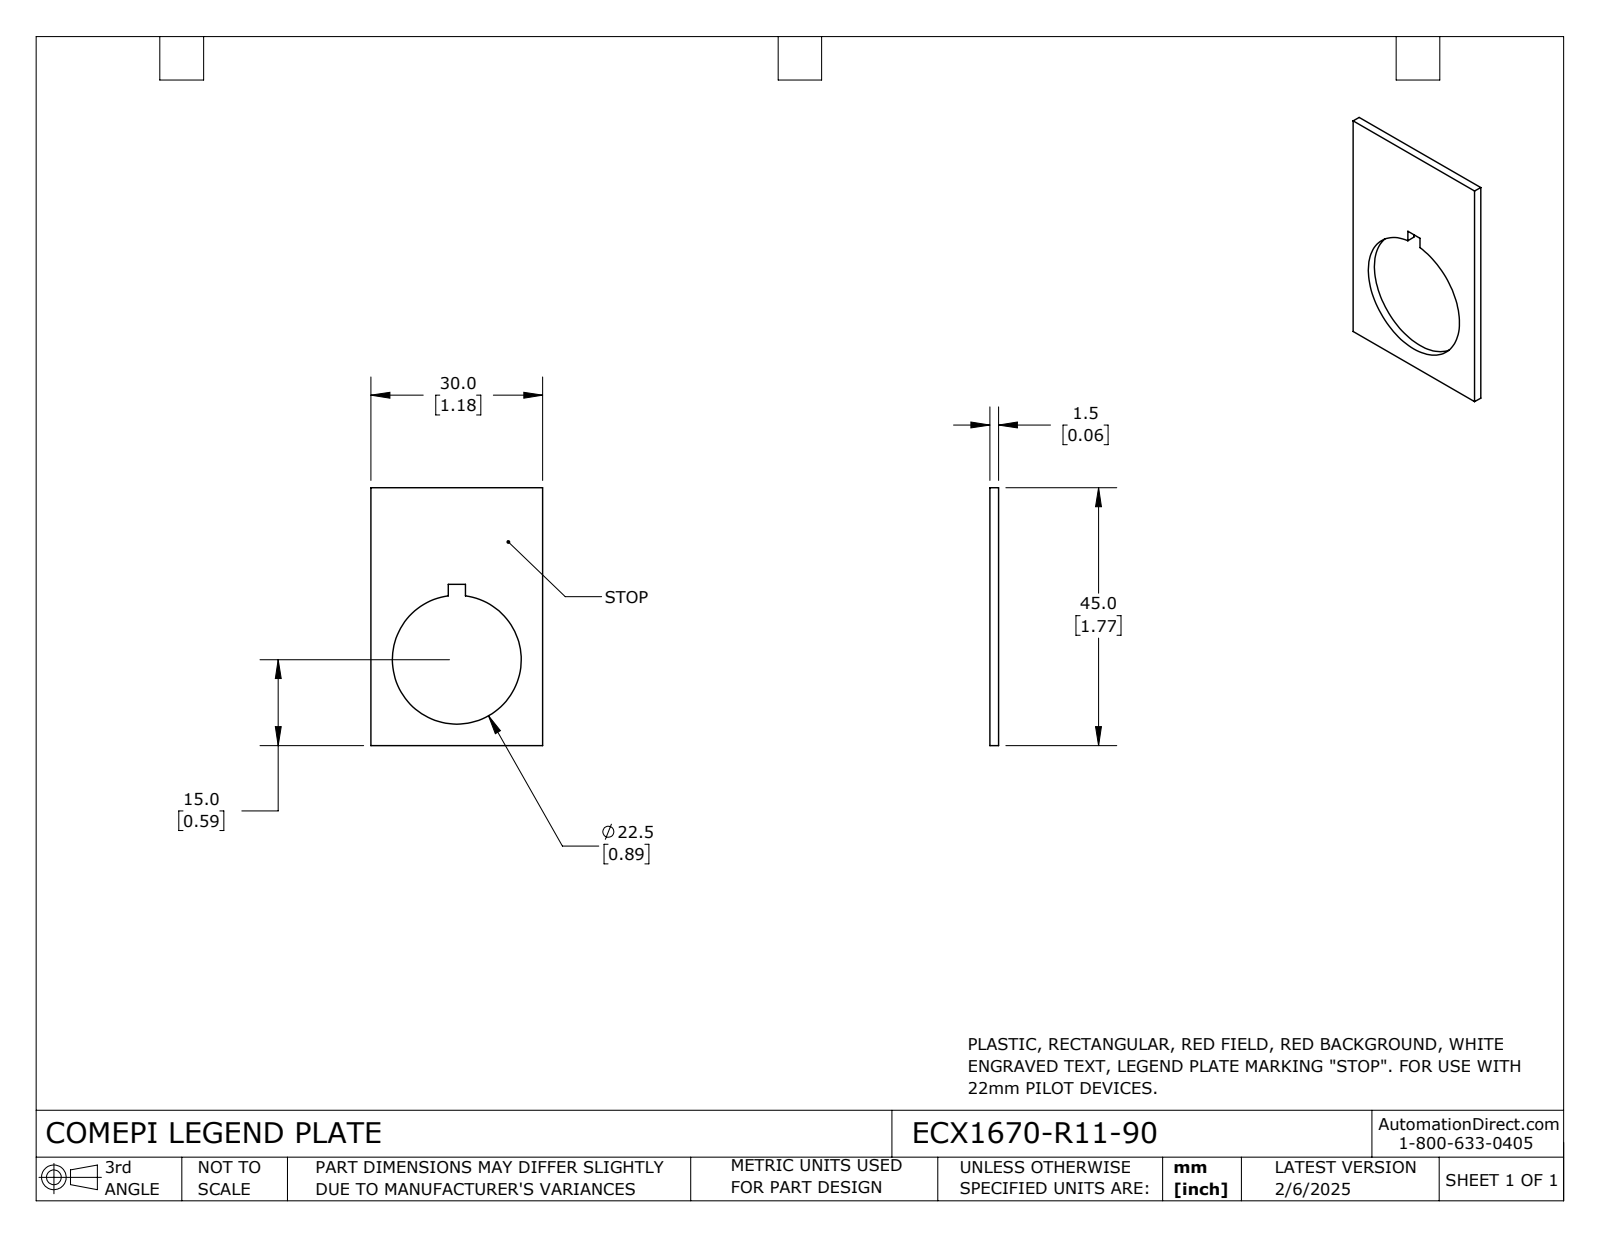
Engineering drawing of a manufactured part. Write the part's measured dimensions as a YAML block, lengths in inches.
part_name: "ECX1670-R11-90"
step_written_by: "SolidWorks 2024 (CONFIG_CONTROL_DESIGN)"
units: inches
bodies: {solids: 1, faces: 12, planar: 9, cylindrical: 3, other: 0}
overall_size: [1.772, 1.181, 0.059]
volume: 0.087
surface_area: 3.457
round_holes:
  - {diameter: 0.886, count: 1}
face_to_face_distances: [0.059, 1.181, 1.772, 0.531, 0.65, 1.108, 0.663, 0.118]
